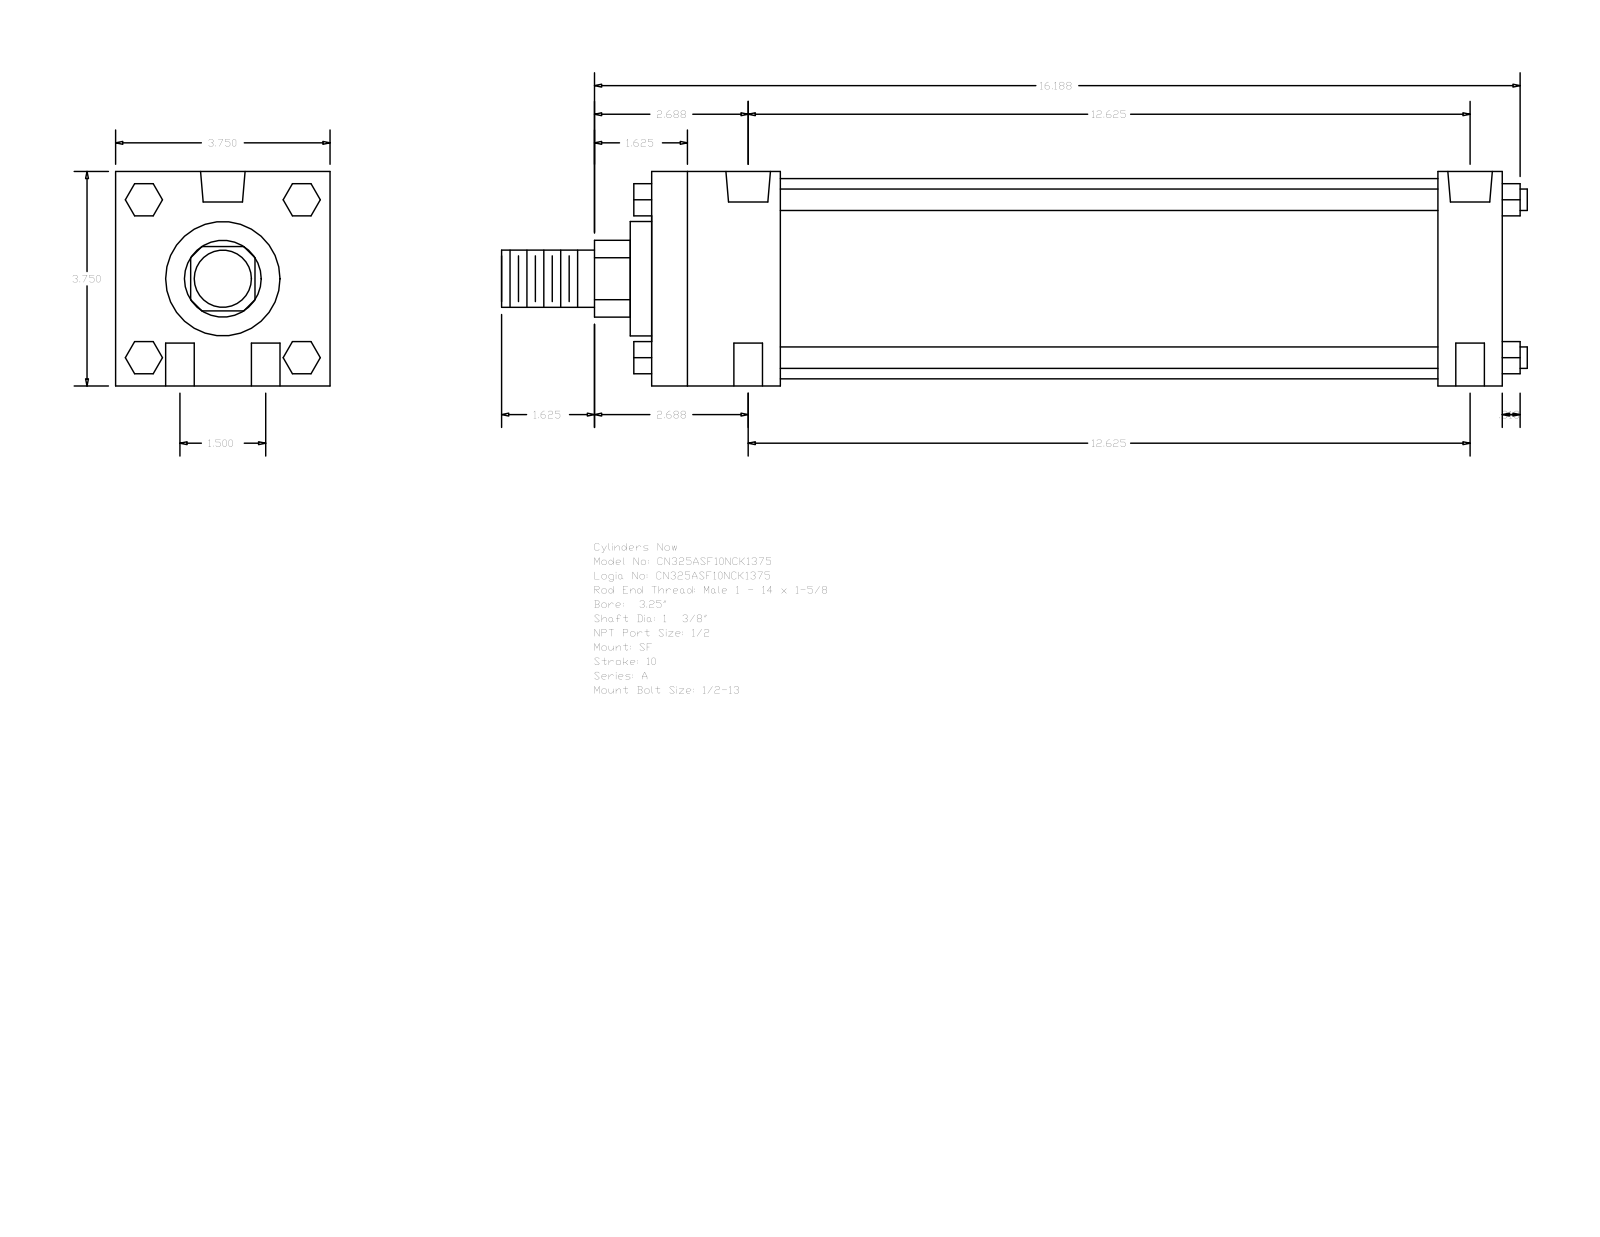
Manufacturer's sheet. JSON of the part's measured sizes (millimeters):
{"part_name": "A_SF__0325_1.375", "step_written_by": "GSSL Pune (CONFIG_CONTROL_DESIGN)", "units": "millimeters", "bodies": {"solids": 0, "faces": 124, "planar": 94, "cylindrical": 30, "other": 0}, "overall_size": [455.61, 95.25, 95.25], "round_holes": [[12.7, 4], [8.73, 2], [19.77, 2]], "round_bosses_or_shafts": [[9.53, 4], [88.9, 1], [50.8, 1], [34.92, 1], [25.4, 1]], "partial_cylinders_radius": [[17.06, 1]], "face_to_face_distances": [95.24, 377.83, 57.15, 28.58, 349.25, 292.1, 320.68, 66.67, 9.52, 358.77], "hole_center_spacings": [19.05, 321.25, 320.68, 38.1, 322.94, 314.32]}
